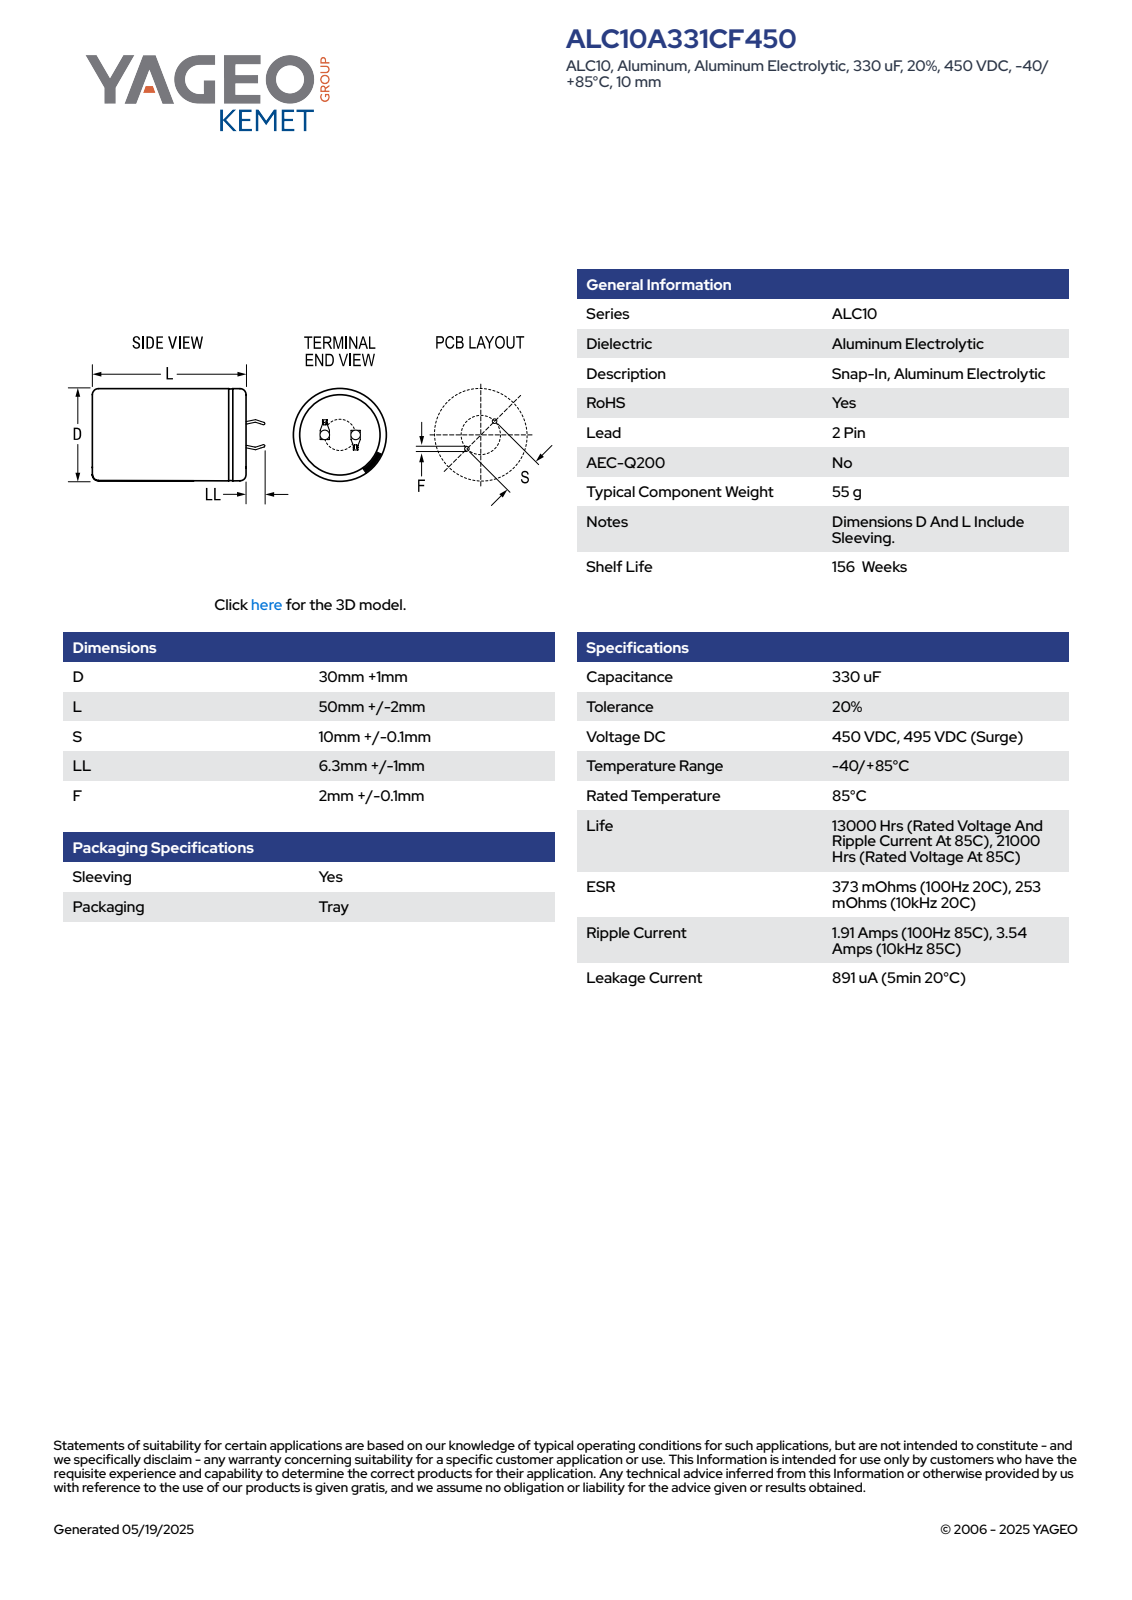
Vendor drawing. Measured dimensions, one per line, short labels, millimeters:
name: CARS_K2P_30X50_D31L52S10LL7.3F2.1
written by: SolidWorks 2014 (AUTOMOTIVE_DESIGN)
unit: mm
bodies: 1 solid, 100 faces (52 planar, 9 cylindrical, 39 other)
size: 59.29 × 31 × 31
volume: 38 914 mm³; area: 6 584 mm²
holes: 1× ⌀27.43
bosses: 1× ⌀31
rounds: 1× R15.49
face distances: 51.99, 0.6, 52.49, 0.5, 7.08, 7.64, 0.75, 1.35, 7.68, 6.48
